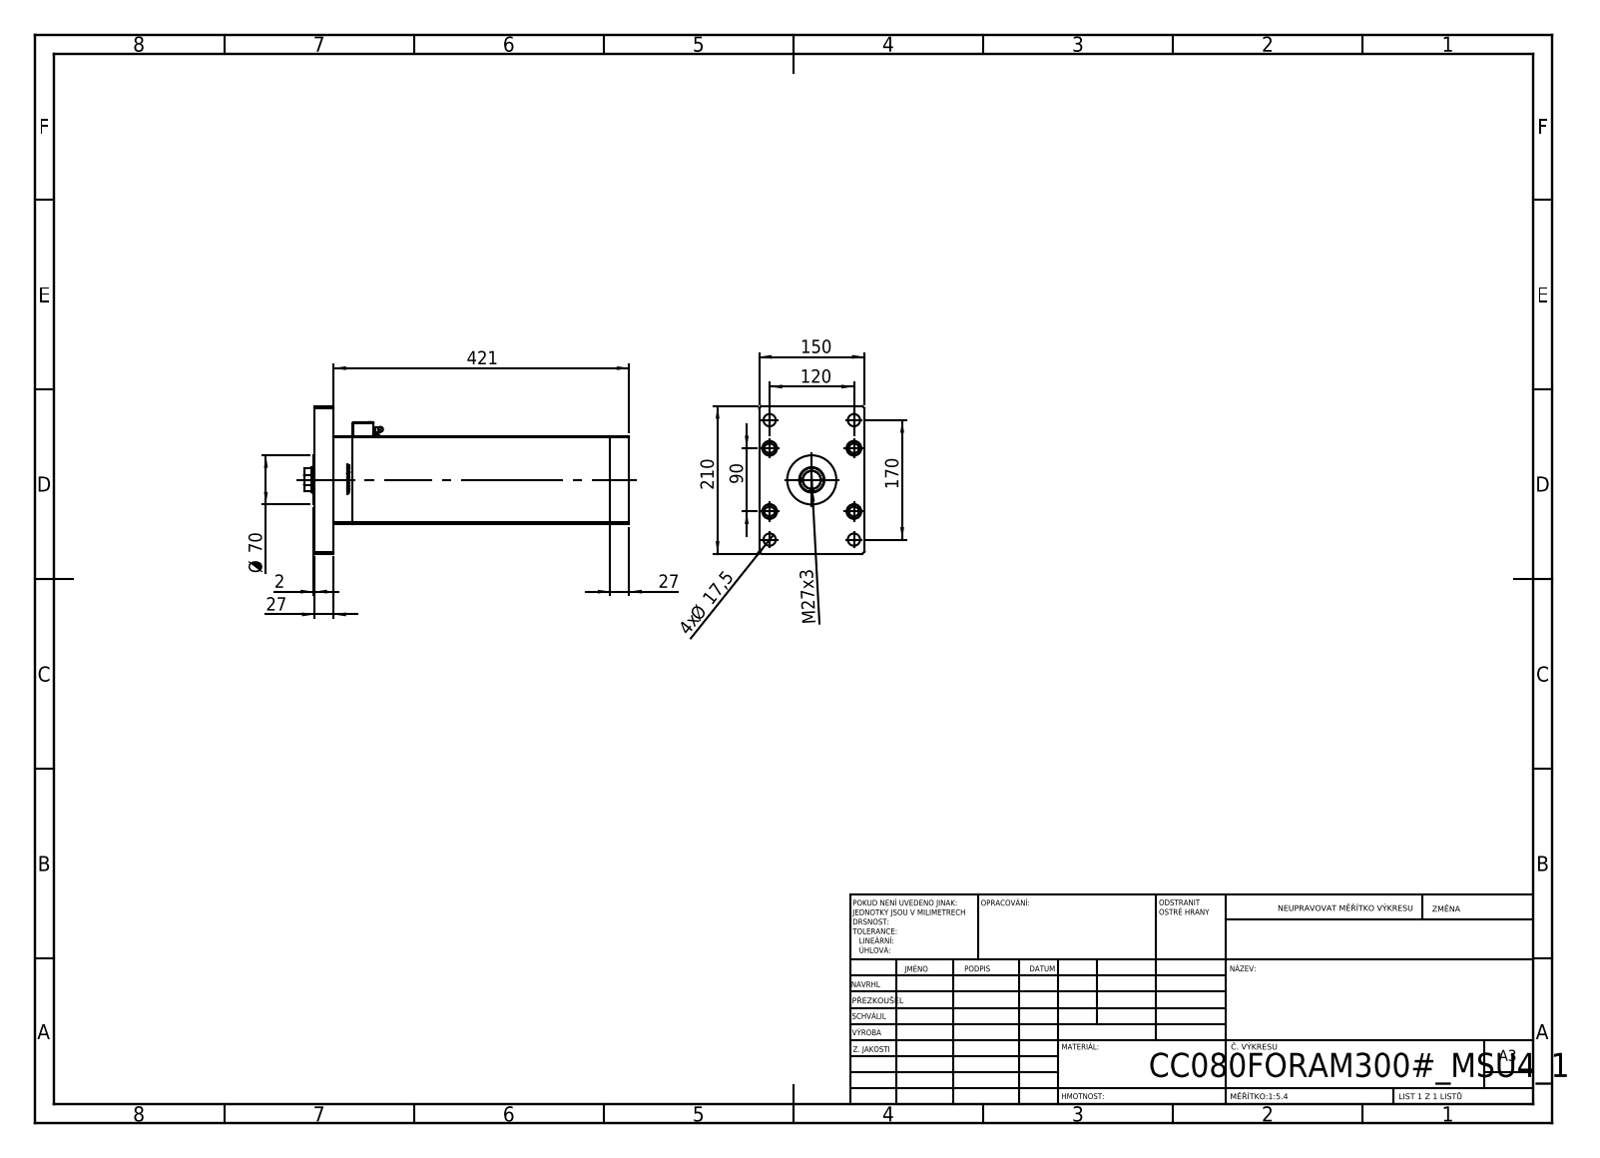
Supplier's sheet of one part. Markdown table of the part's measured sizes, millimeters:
| quantity | value |
| --- | --- |
| part name | V220C_F; ALLEN BOLT; V220C_F_MIDDLE; V220C_VC_F (+3 more) |
| STEP written by | SolidWorks 2019 (CONFIG_CONTROL_DESIGN) |
| units | millimeters |
| bodies | 20 solids, 1400 faces (552 planar, 224 cylindrical, 624 other) |
| overall size | 463 × 210 × 150 |
| volume | 7 294 000 mm³ |
| surface area | 663 267 mm² |
| round holes (diameter × count) | 17.5 × 9, 22 × 5, 16 × 4, 21 × 4, 3.6 × 1, 5 × 1, 7 × 1, 25.5 × 1, 36 × 1, 37.5 × 1 |
| round bosses / shafts (diameter × count) | 8 × 9, 21 × 5, 0.85 × 4, 7 × 2, 80 × 1, 70 × 1, 6 × 1, 3.5 × 1 |
| partial cylindrical surfaces (radius × count) | 1 × 14, 0.93 × 2, 4 × 2, 17.5 × 1 |
| main face-to-face distances | 27, 150, 125, 394, 421, 54, 367, 448, 6.5, 33.5 |
| hole center spacings | 51, 40, 75, 104.04, 120, 126.49, 130, 176.92 |
